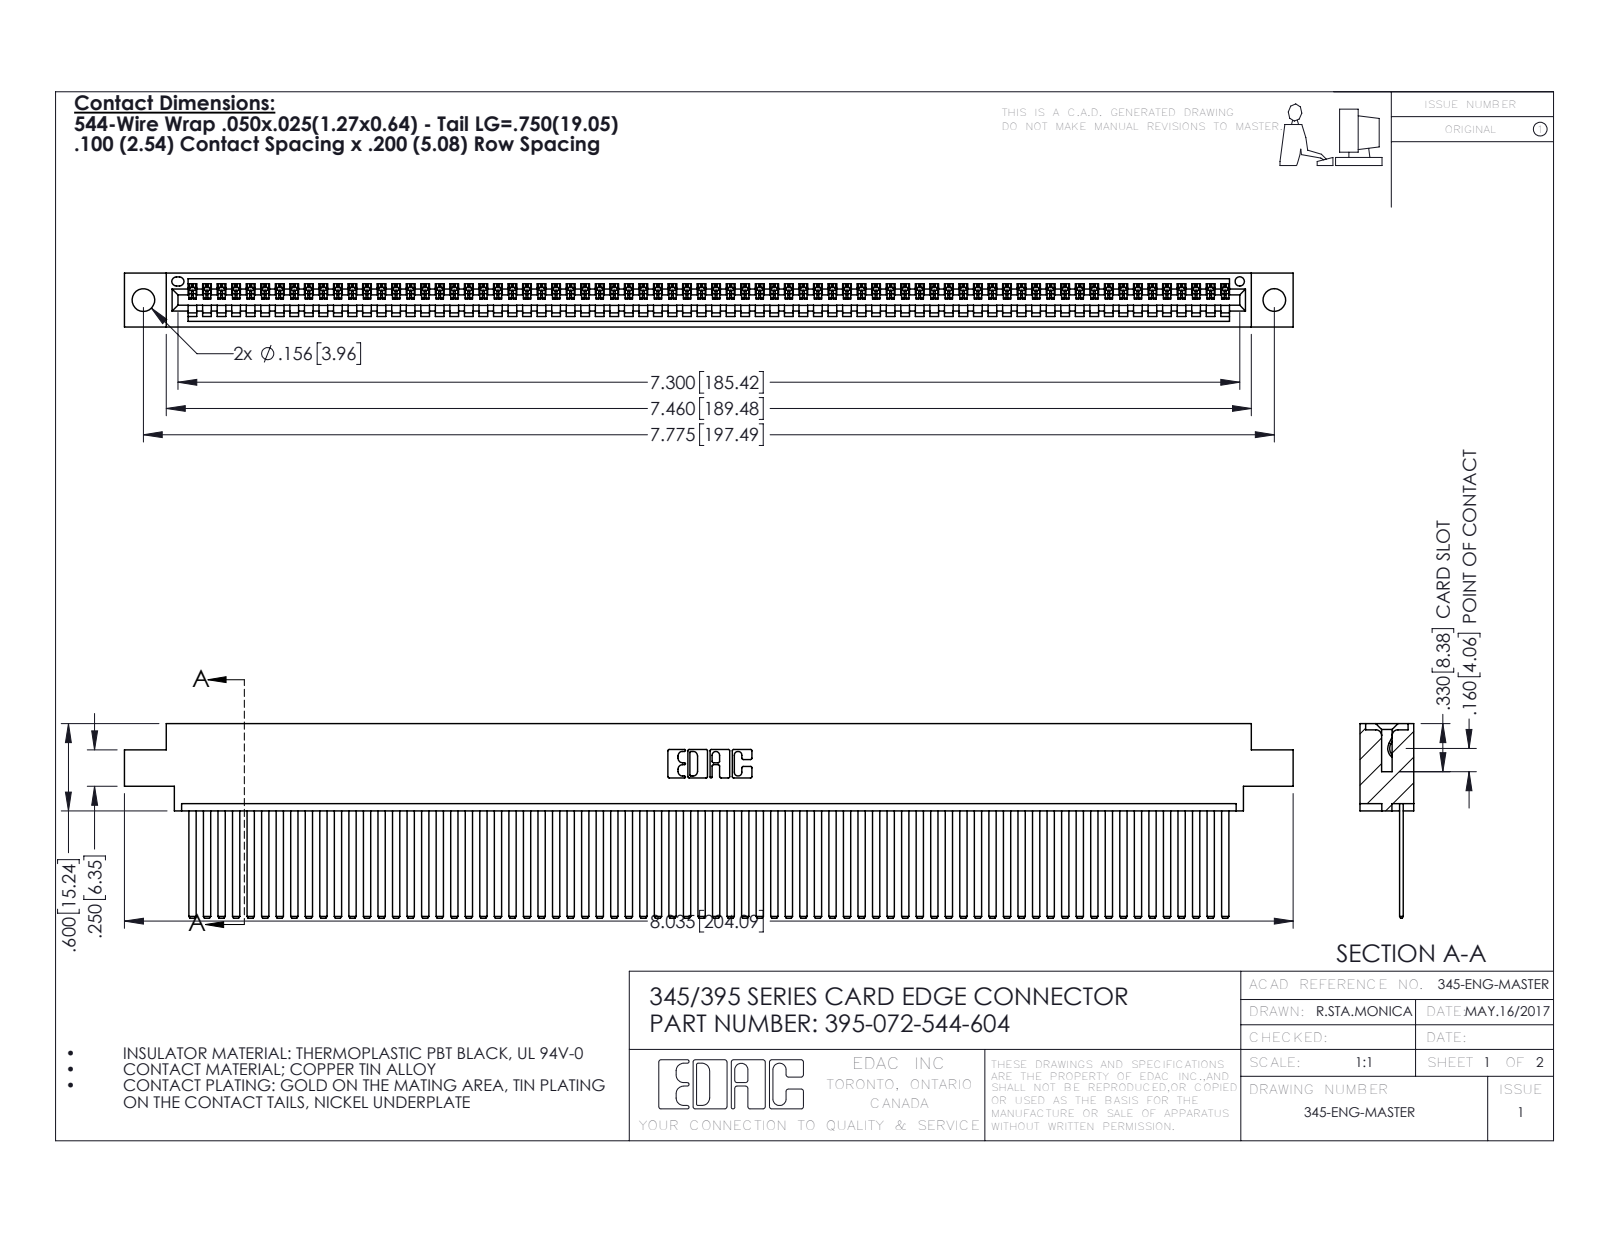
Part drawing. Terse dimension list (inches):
name: 395-072-544-604; 345 Part_0.170 Offset - 0.156 Dia-TH; 345-292-001_345-293-144
written by: SolidWorks 2016 (CONFIG_CONTROL_DESIGN)
unit: in
bodies: 73 solids, 3874 faces (2676 planar, 1198 cylindrical, 0 other)
size: 8.035 × 1.337 × 0.37
volume: 1.237 in³; area: 46.15 in²
holes: 2× ⌀0.156, 1× ⌀0.064
rounds: 144× R0.006, 22× R0.01, 6× R0.007, 6× R0.031, 3× R0.026, 2× R0.031, 2× R0.04, 1× R0.014
face distances: 0.072, 0.298, 0.025, 0.098, 0.272, 0.37, 0.2, 0.225, 0.149, 0.175
hole spacings: 0.27, 7.539, 7.775
